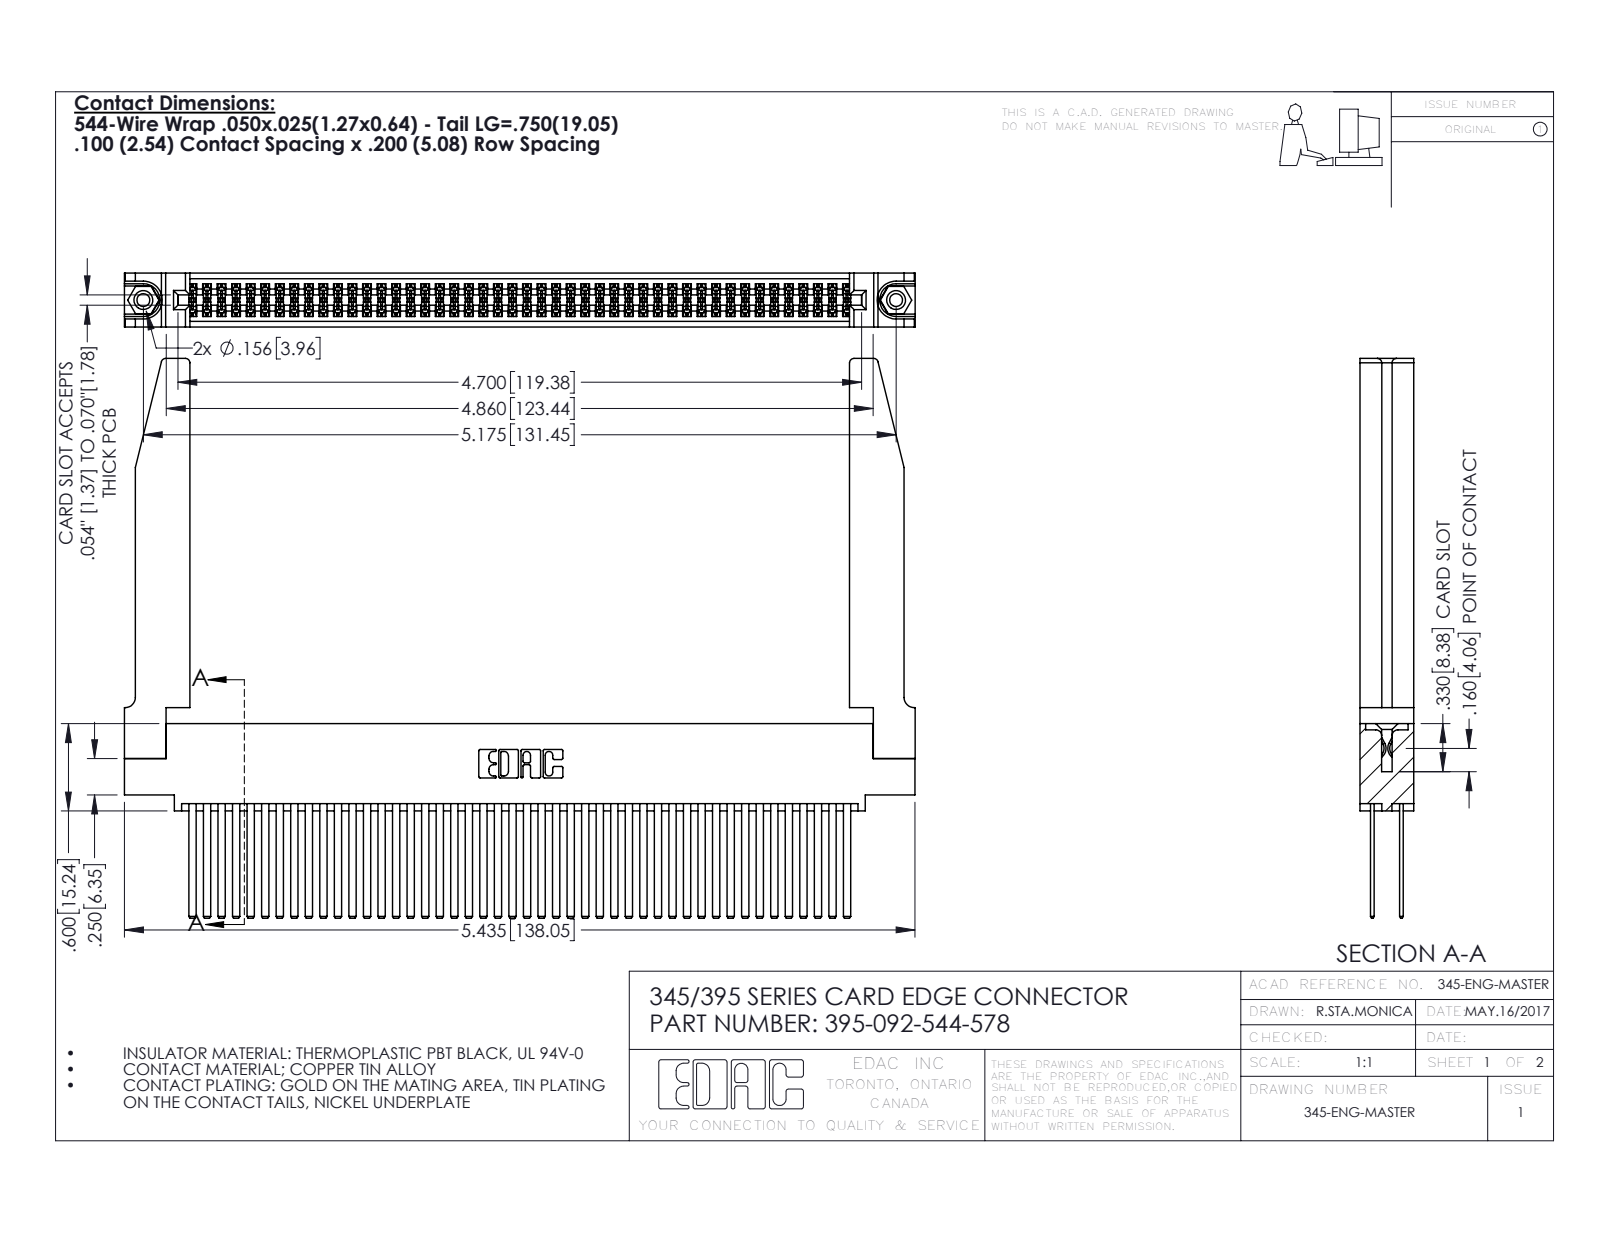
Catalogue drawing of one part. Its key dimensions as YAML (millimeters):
part_name: "345-250-001_345-250-001-102; 395-092-544-578; 345 Part_0.110 Offset - 0.156 Dia-TH; 345-220-078_345-220-078 (+1 more)"
step_written_by: "SolidWorks 2016 (CONFIG_CONTROL_DESIGN)"
units: millimeters
bodies: {solids: 97, faces: 4412, planar: 2894, cylindrical: 1466, other: 52}
overall_size: [138.1, 97.7, 9.4]
volume: 22430
surface_area: 32460
round_holes:
  - {diameter: 2.3, count: 2}
  - {diameter: 3.2, count: 2}
  - {diameter: 4, count: 2}
  - {diameter: 1.6, count: 1}
round_bosses_or_shafts:
  - {diameter: 3.9, count: 2}
partial_cylinders:
  - {radius: 0.2, count: 138}
  - {radius: 0.3, count: 22}
  - {radius: 0.8, count: 8}
  - {radius: 0.2, count: 6}
  - {radius: 0.8, count: 6}
  - {radius: 0.7, count: 3}
  - {radius: 0.4, count: 2}
  - {radius: 0.5, count: 2}
face_to_face_distances: [1.8, 7.6, 2.5, 6.9, 0.6, 5.1, 9.4, 5.7, 4.4, 3.8]
hole_center_spacings: [6.9, 125.5, 131.4]
